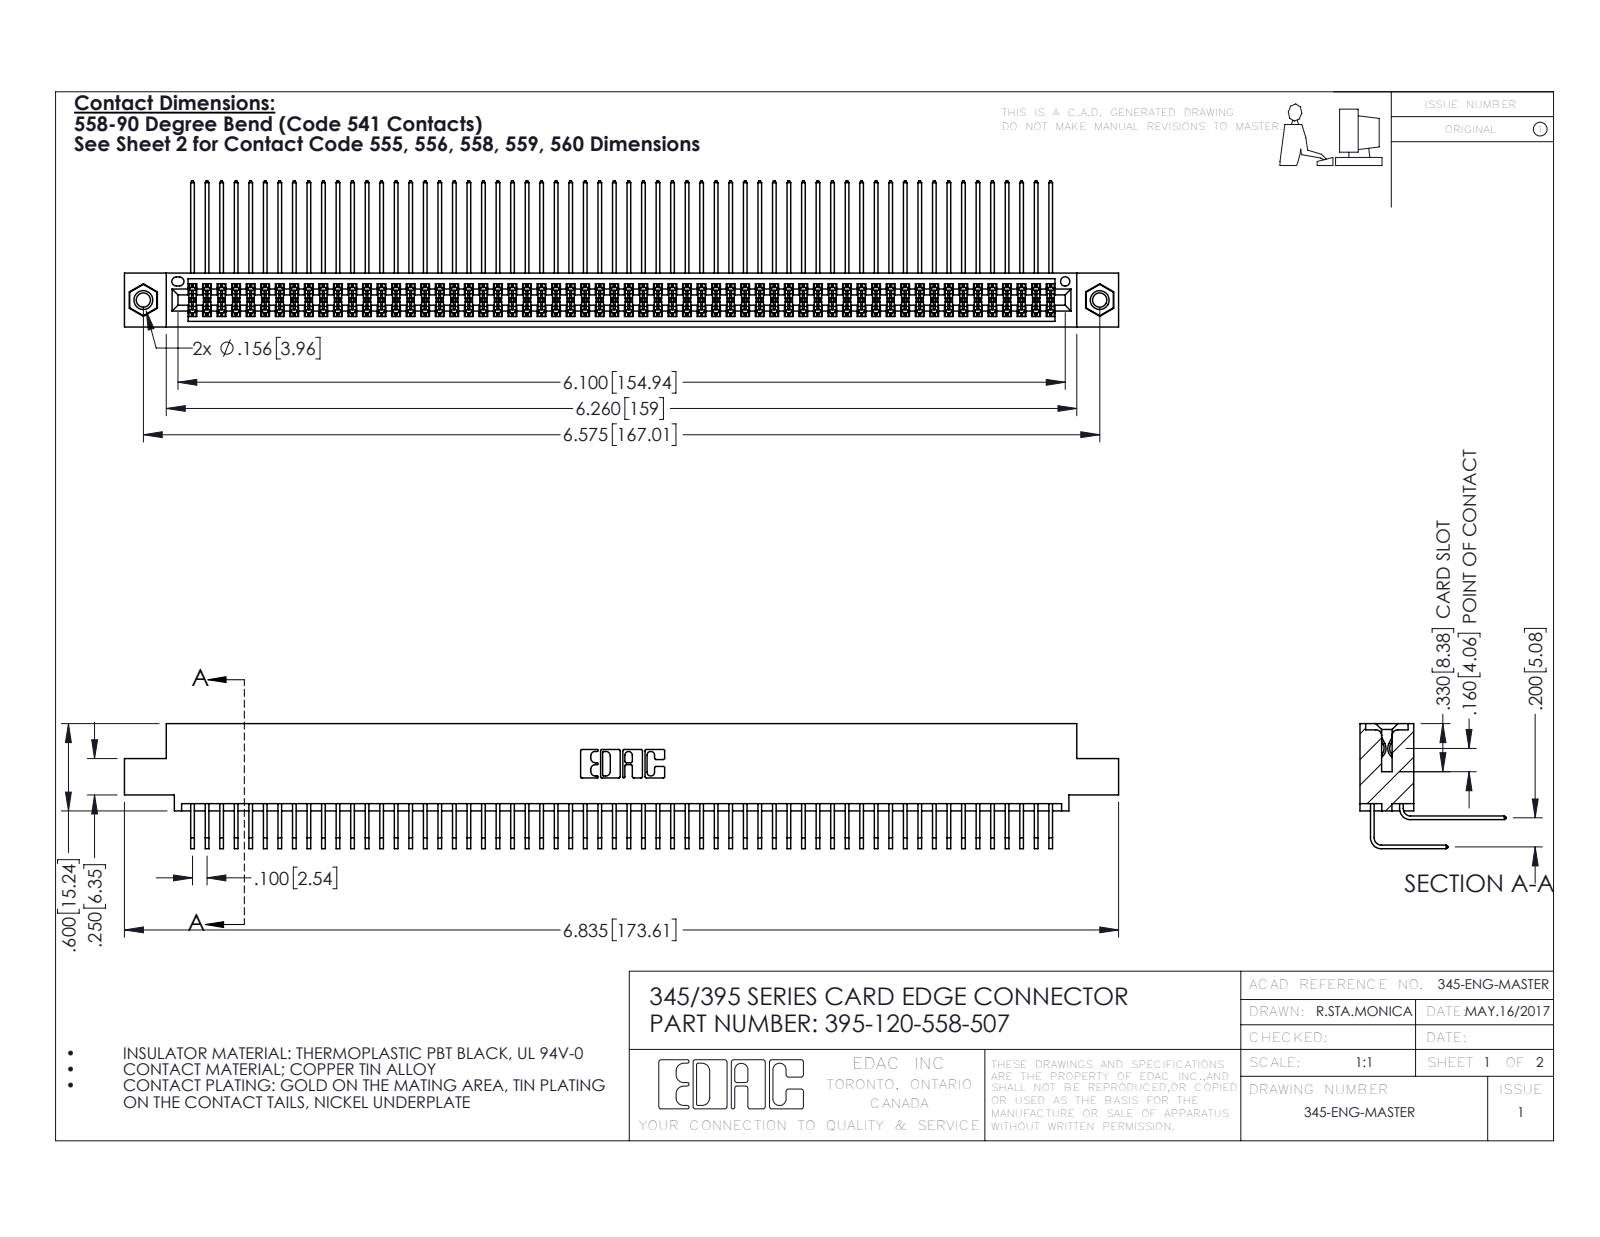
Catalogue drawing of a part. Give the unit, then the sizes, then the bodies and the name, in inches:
Units: inches
Overall size (bounding box): 6.835 × 1.005 × 0.859
Round holes (diameter × count): ⌀0.098 ×2, ⌀0.125 ×2, ⌀0.156 ×2, ⌀0.064 ×1
Round bosses / shafts (diameter × count): ⌀0.155 ×2
Partial cylindrical surfaces — rounded edges, fillets, slot ends (radius × count): R0.006 ×181, R0.01 ×22, R0.007 ×6, R0.031 ×6, R0.026 ×3, R0.014 ×2, R0.019 ×2, R0.022 ×2
Main face-to-face distances: 0.072, 0.298, 0.2, 0.37, 0.098, 0.272, 0.025, 0.225, 0.025, 0.175
Hole centre spacings: 0.27, 6.339, 6.575
Volume: 1.076 in³ · Surface area: 46.18 in²
Bodies: 123 solids, 6430 faces (4316 planar, 2098 cylindrical, 16 other)
Part name (STEP PRODUCT): 395-120-558-507; 345-250-001_345-250-005-103; 345 Part_0.110 Offset - 0.156 Dia-TI; 345-292-001_558 559 Tail - 1 (+1 more)
STEP written by: SolidWorks 2016 (CONFIG_CONTROL_DESIGN)
